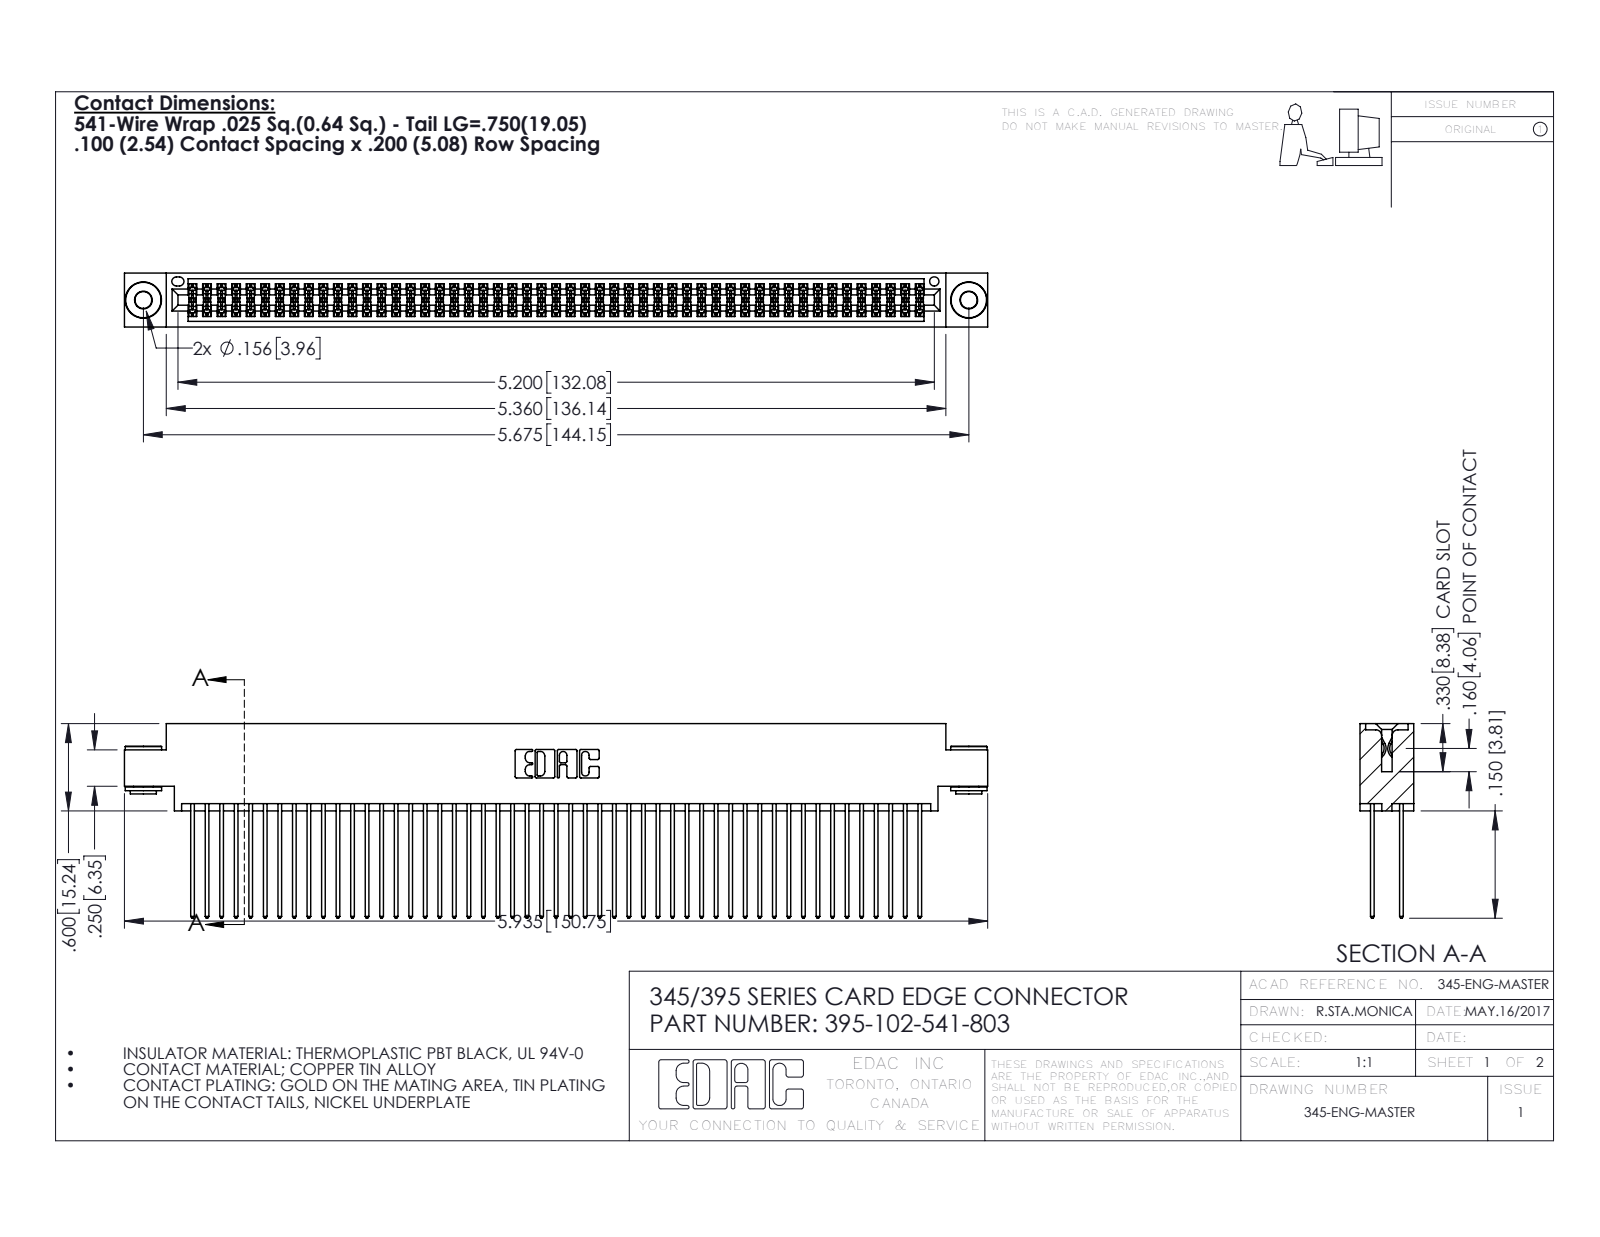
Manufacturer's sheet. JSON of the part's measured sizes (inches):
{"part_name": "345-292-001_345-293-141; 345 Part_0.170 Offset - 0.156 Dia-TH; 395-102-541-803; 345-250-002_345-250-002-102", "step_written_by": "SolidWorks 2016 (CONFIG_CONTROL_DESIGN)", "units": "inches", "bodies": {"solids": 105, "faces": 5268, "planar": 3460, "cylindrical": 1800, "other": 8}, "overall_size": [5.935, 1.337, 0.37], "volume_in3": 0.929, "surface_area_in2": 39.94, "round_holes": [[0.116, 2], [0.156, 2], [0.064, 1]], "round_bosses_or_shafts": [[0.25, 2], [0.18, 2], [0.136, 2]], "partial_cylinders_radius": [[0.006, 153], [0.01, 102], [0.01, 22], [0.007, 6], [0.031, 6], [0.026, 3], [0.014, 2], [0.019, 2]], "face_to_face_distances": [0.072, 0.298, 0.2, 0.098, 0.272, 0.025, 0.37, 0.225, 0.175, 0.149], "hole_center_spacings": [0.27, 5.439, 5.675]}
